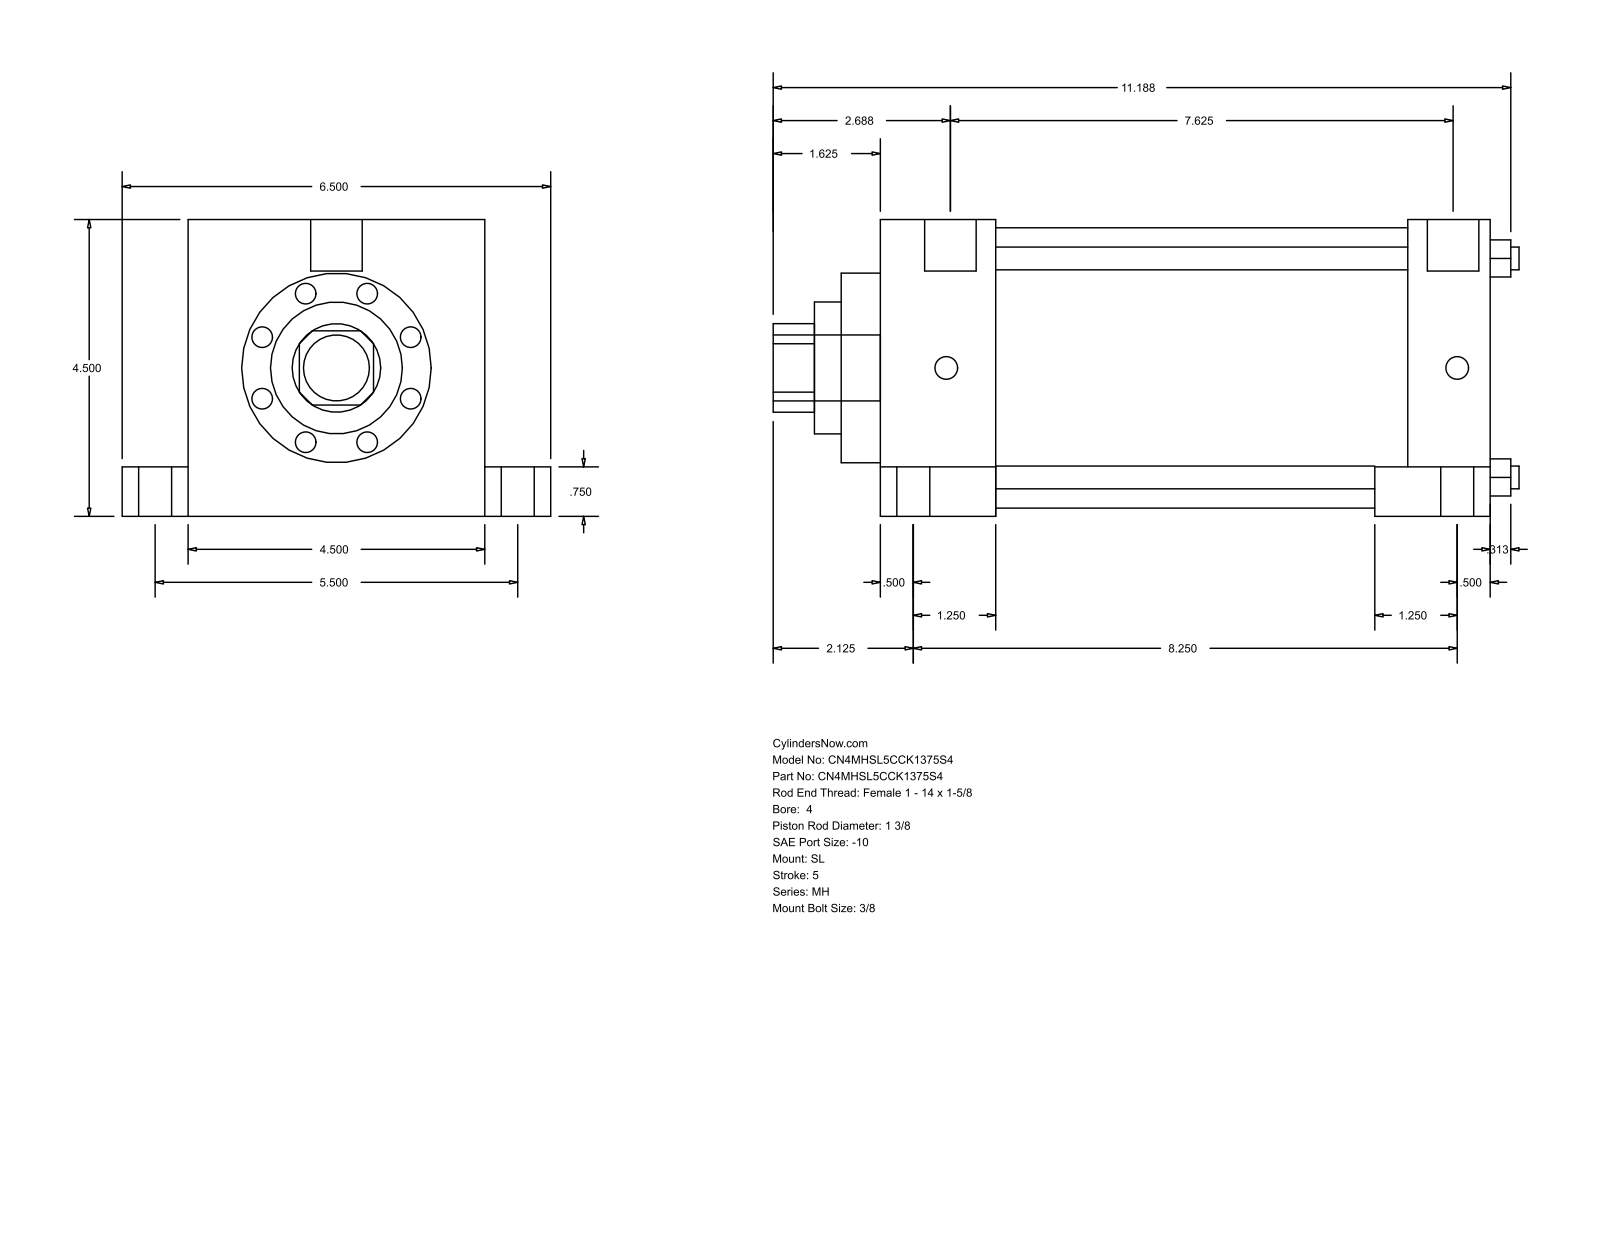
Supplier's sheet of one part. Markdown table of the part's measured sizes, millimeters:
| quantity | value |
| --- | --- |
| part name | MH_SL__0400_1.375 |
| STEP written by | GSSL Pune (CONFIG_CONTROL_DESIGN) |
| units | millimeters |
| bodies | 0 solids, 110 faces (77 planar, 33 cylindrical, 0 other) |
| overall size | 287.34 × 165.1 × 114.3 |
| round holes (diameter × count) | 8.76 × 4, 34.92 × 1, 50.8 × 1, 73.03 × 1, 107.95 × 1 |
| round bosses / shafts (diameter × count) | 19.05 × 4, 12.7 × 4, 8.73 × 4, 19.84 × 2, 25.4 × 1 |
| partial cylindrical surfaces (radius × count) | 17.06 × 1 |
| main face-to-face distances | 114.3, 234.96, 44.45, 190.51, 203.2, 158.75, 31.76, 25.4, 139.7, 19.05 |
| hole center spacings | 59.62, 84.32, 119.25 |
